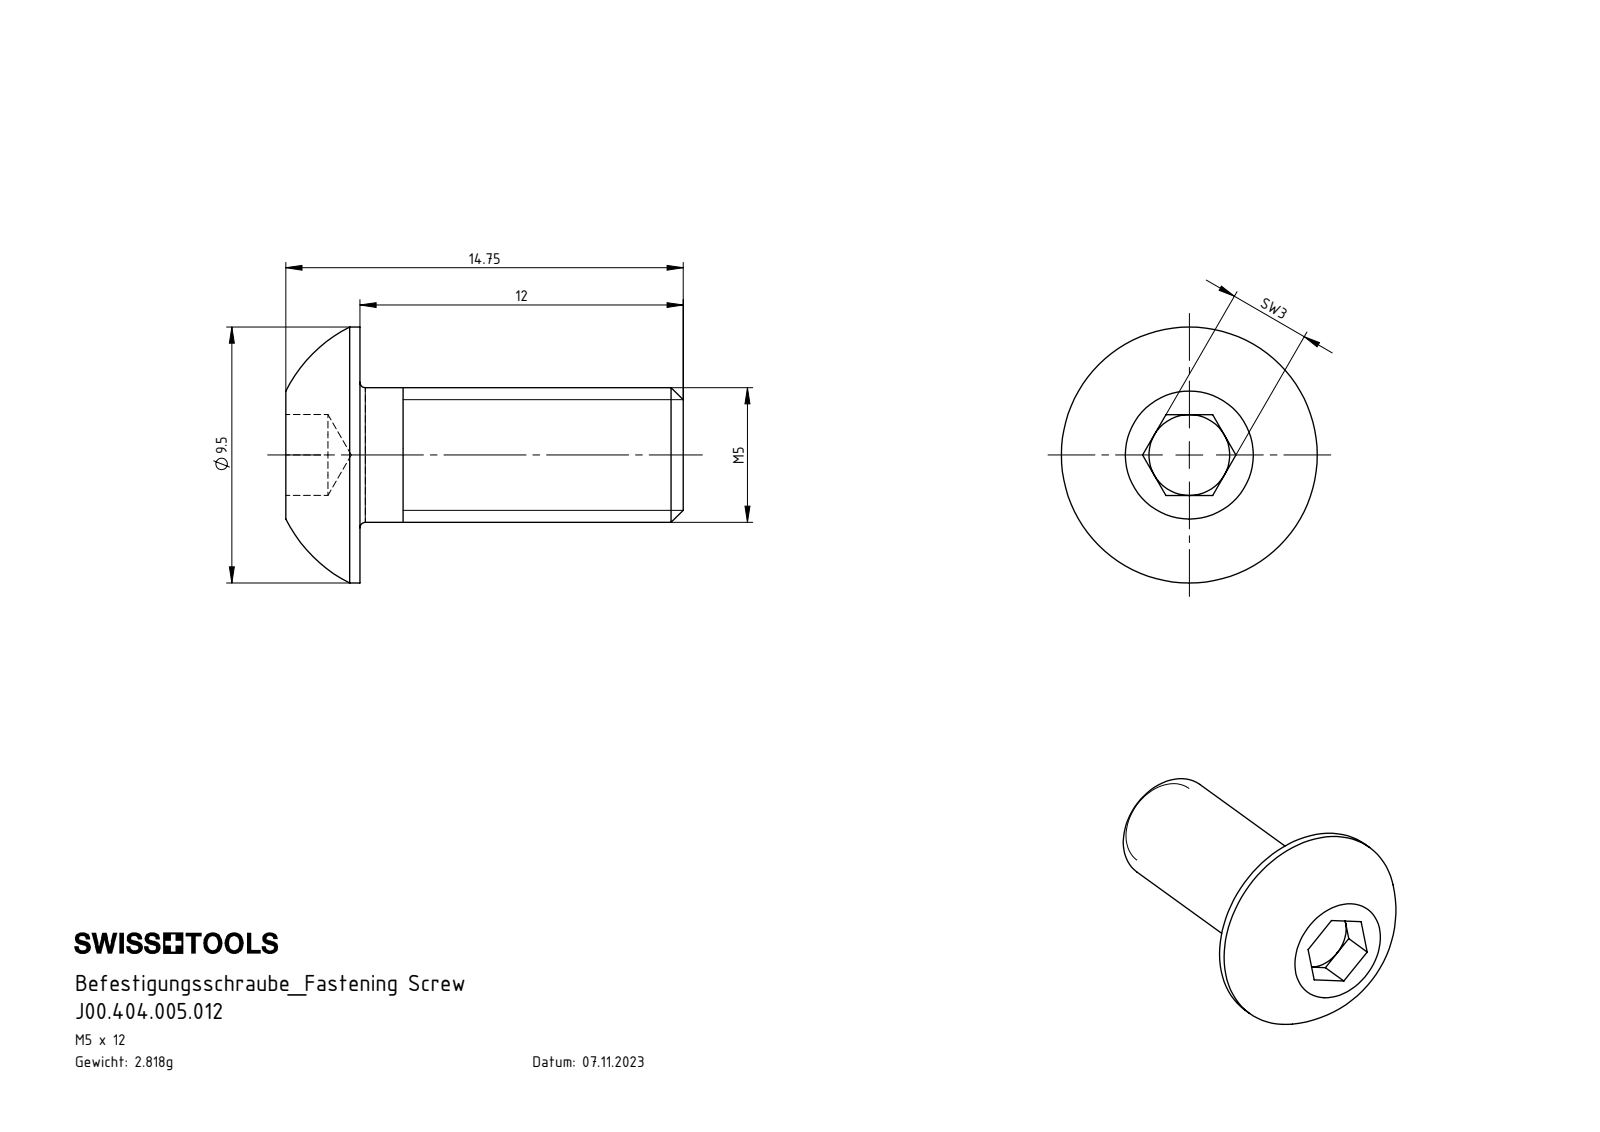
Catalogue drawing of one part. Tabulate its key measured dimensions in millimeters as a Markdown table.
| quantity | value |
| --- | --- |
| part name | J00.404.005.012 |
| STEP written by | SolidWorks 2022 (AUTOMOTIVE_DESIGN) |
| units | millimeters |
| bodies | 1 solid, 27 faces (15 planar, 4 cylindrical, 8 other) |
| overall size | 14.75 × 9.5 × 9.5 |
| volume | 359 mm³ |
| surface area | 379 mm² |
| round bosses / shafts (diameter × count) | 9.5 × 1, 5 × 1 |
| main face-to-face distances | 12, 2.75, 14.75, 3, 1.56, 1.19, 13.19 |
